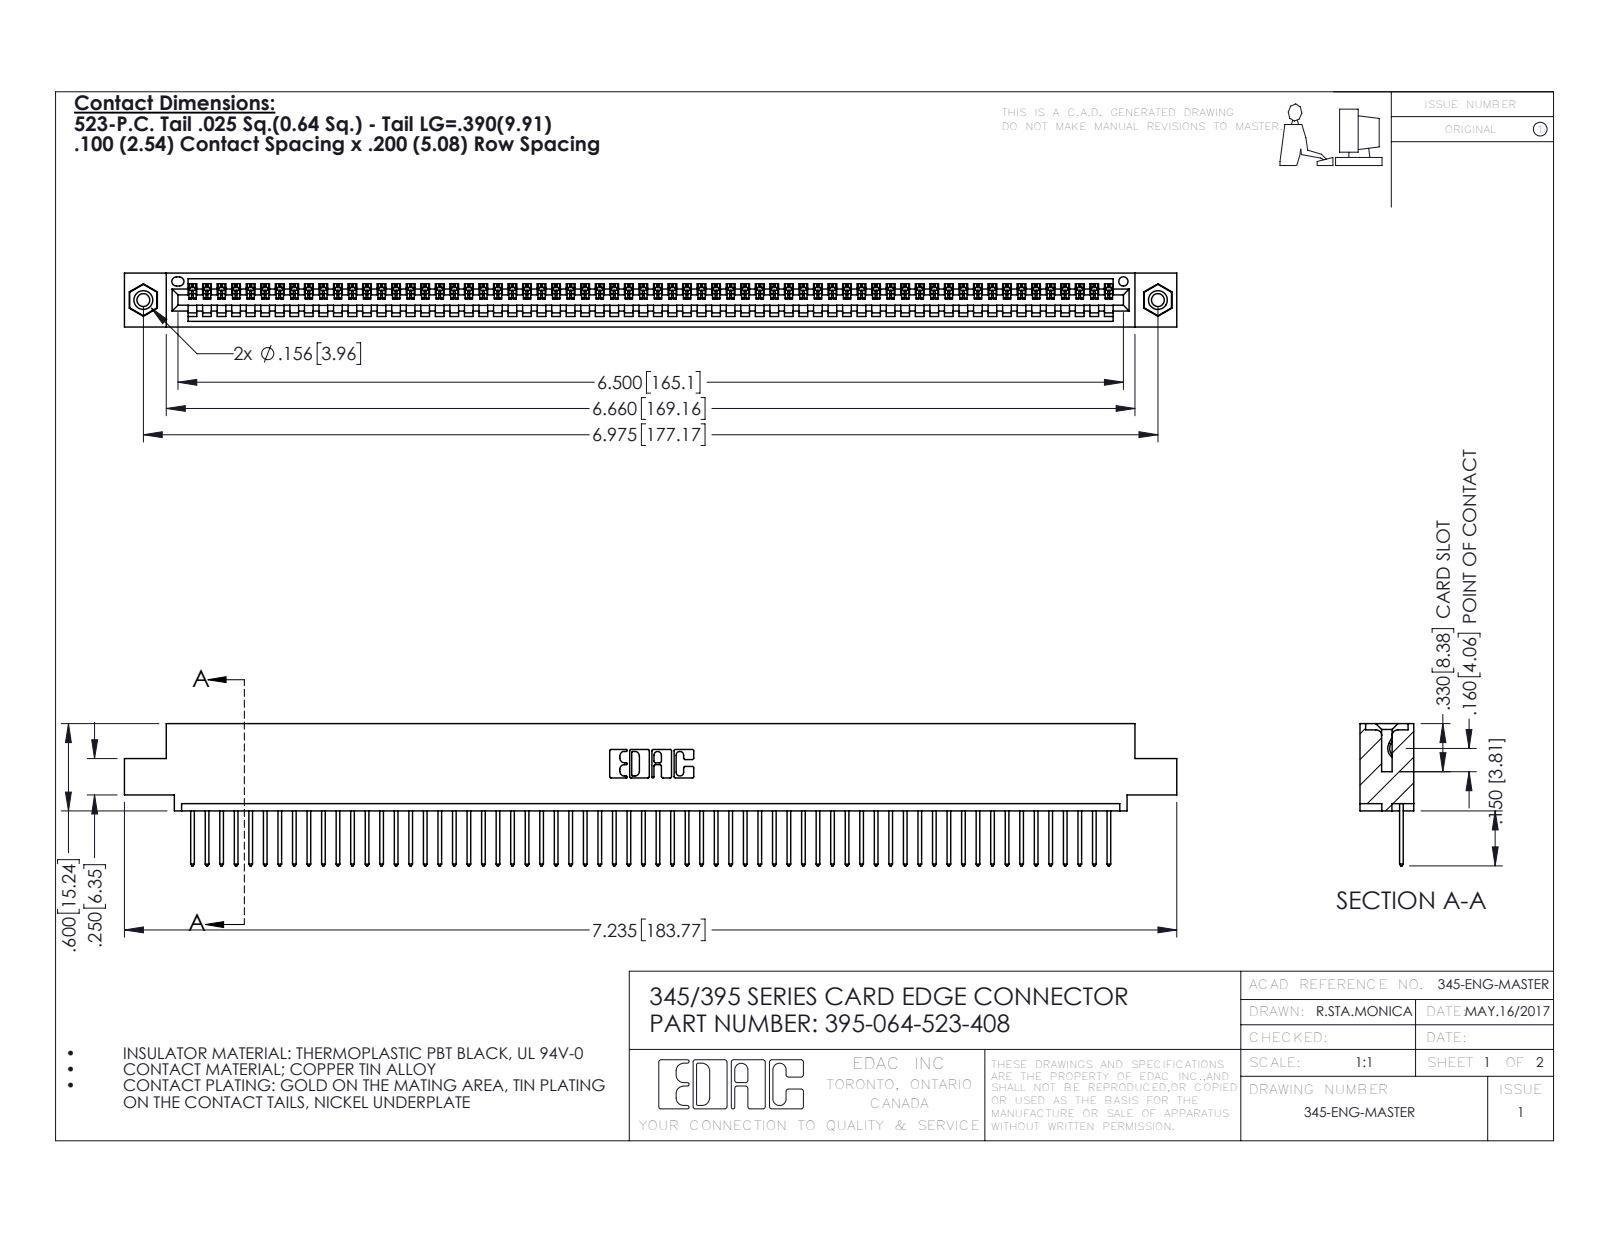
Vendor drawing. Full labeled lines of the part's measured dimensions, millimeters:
Part name (STEP PRODUCT): 395-064-523-408; 345-250-001_345-250-003-102; 345 Part_0.110 Offset - 0.156 Dia-TI; 345-292-001_345-293-123
STEP written by: SolidWorks 2016 (CONFIG_CONTROL_DESIGN)
Units: millimetres
Bodies: 67 solids, 3902 faces (2676 planar, 1210 cylindrical, 16 other)
Overall size (bounding box): 183.8 × 24.8 × 9.4
Volume: 17 530 mm³ · Surface area: 23 770 mm²
Round holes (diameter × count): ⌀2.3 ×2, ⌀3.2 ×2, ⌀4 ×2, ⌀1.6 ×1
Round bosses / shafts (diameter × count): ⌀3.9 ×2
Partial cylindrical surfaces — rounded edges, fillets, slot ends (radius × count): R0.2 ×128, R0.3 ×128, R0.3 ×22, R0.2 ×6, R0.8 ×6, R0.7 ×3, R0.8 ×2, R1 ×2
Main face-to-face distances: 1.8, 7.6, 9.4, 2.5, 6.9, 0.6, 5.1, 5.7, 3.8, 1.8
Hole centre spacings: 6.9, 171.2, 177.2
